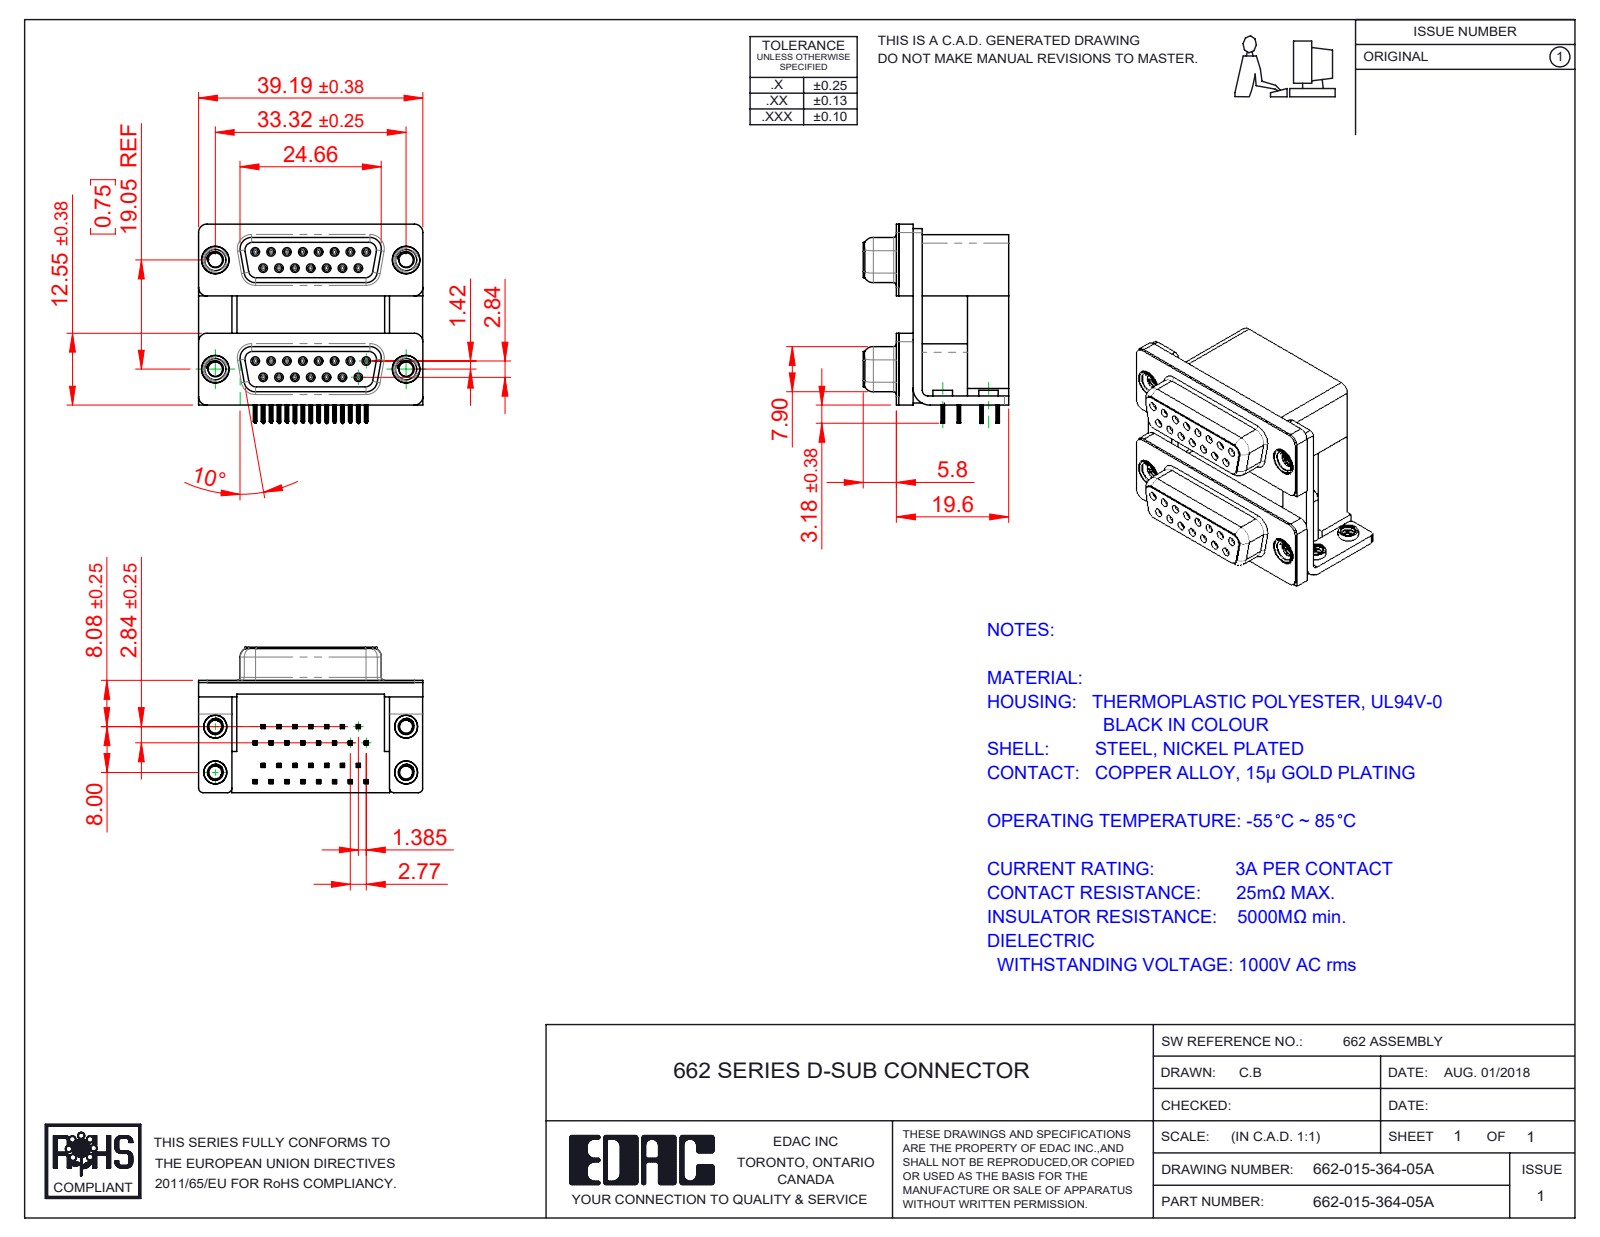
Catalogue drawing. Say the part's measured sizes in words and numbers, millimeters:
The part is named "662 Mounting Bracket_ThruM; 662-015-364-05A; 662 Housing Lower_15 Contacts; 662 Shell_15 Contacts (+8 more)". Its 3-D file was written by "SolidWorks 2020 (CONFIG_CONTROL_DESIGN)". It is 45 solids with 5006 faces: 2208 planar, 1258 cylindrical and 1540 other. Overall it measures 39.19 by 34.78 by 25.4 millimeters. Its volume is 16 037 cubic millimeters and its surface area 18 193 square millimeters. Round holes: 30 of diameter 0.8, 30 of diameter 0.9, 4 of diameter 2.26, 4 of diameter 2.5, 4 of diameter 2.75, 4 of diameter 3.2, 4 of diameter 3.5, 4 of diameter 4, 4 of diameter 4.8, 4 of diameter 5. Round bosses or shafts: 30 of diameter 1.2, 4 of diameter 4.9, 4 of diameter 4.75, 4 of diameter 4, 4 of diameter 3.9, 4 of diameter 3.4. Partial cylindrical surfaces (rounded edges, fillets, slot ends): 240 of radius 0.1, 120 of radius 0.15, 60 of radius 0.35, 30 of radius 0.34, 16 of radius 1.35, 16 of radius 1.5, 14 of radius 0.28, 8 of radius 0.5. The main face-to-face distances are 19.05, 0.4, 19.2, 12, 2.5, 16.7, 7.2, 9.5, 2.9, 10.7. The hole center spacings are 3.16, 19.25, 2.77, 19.84, 5.54, 8.31, 19.05, 20.78.
